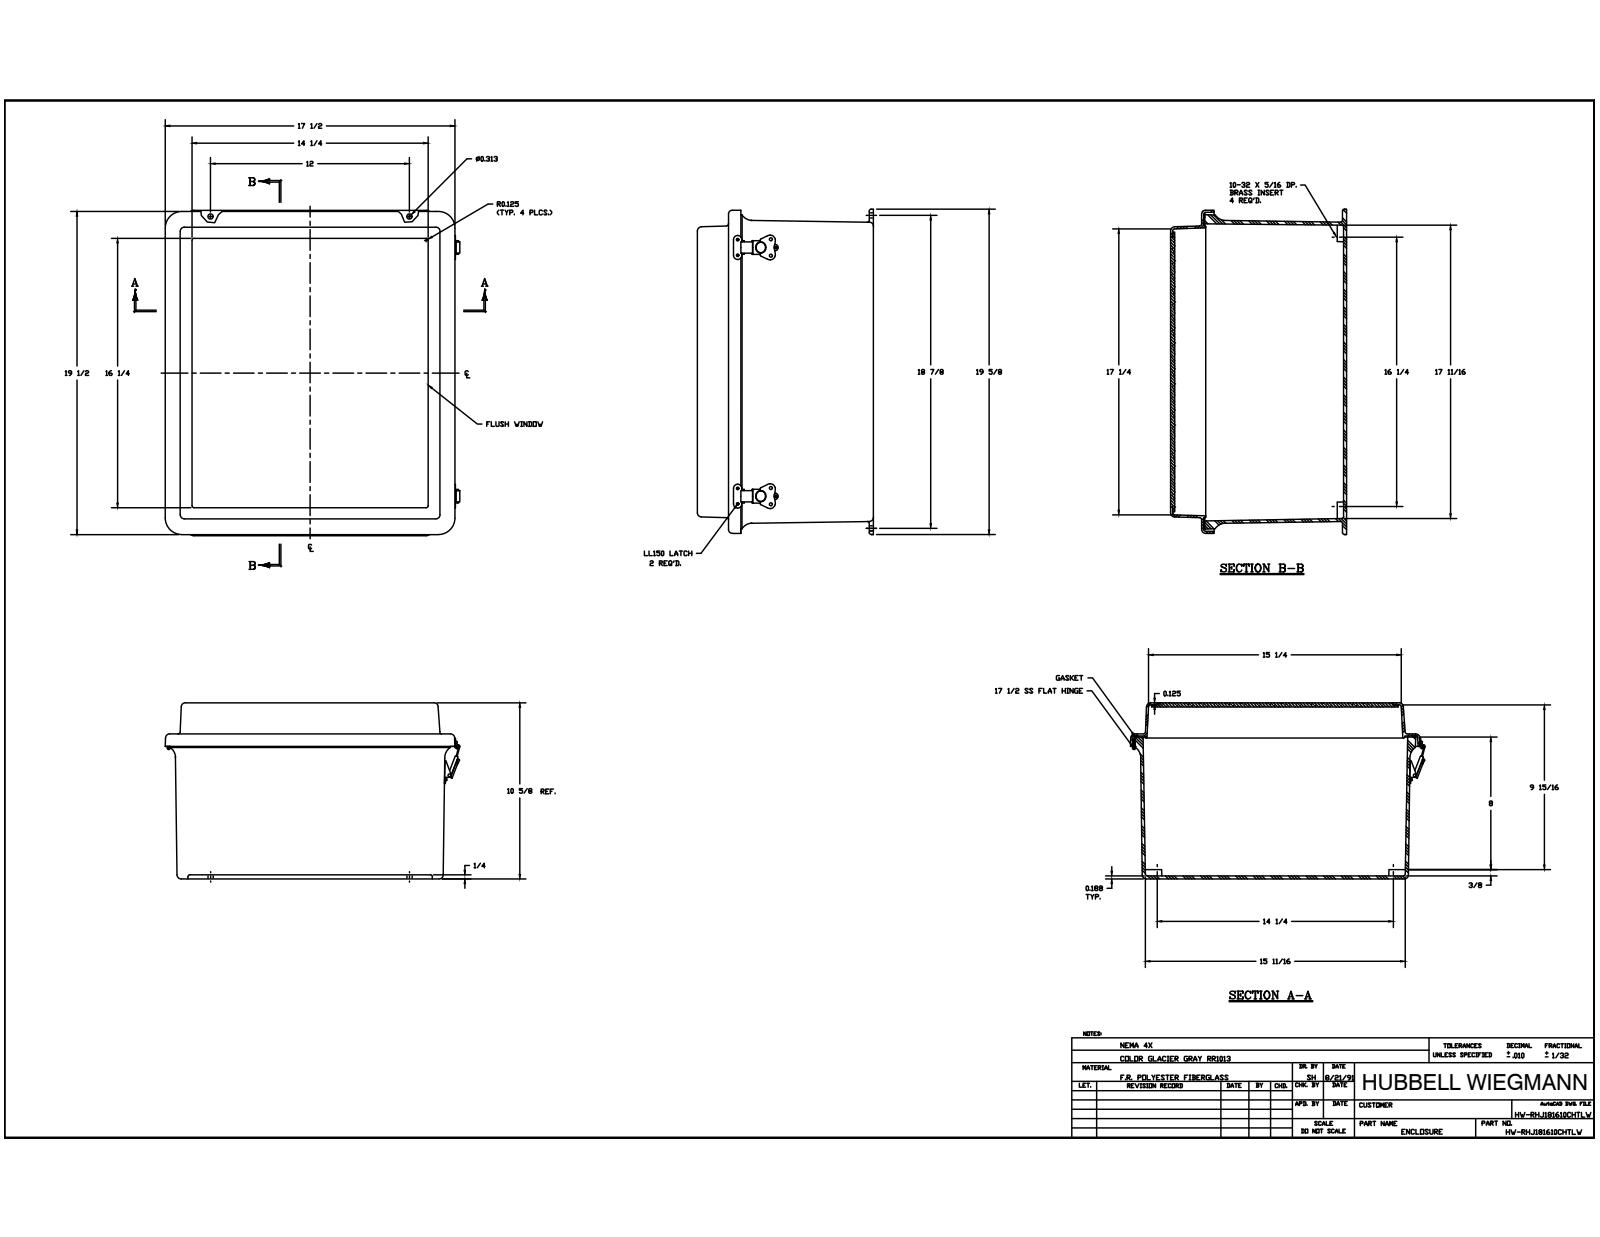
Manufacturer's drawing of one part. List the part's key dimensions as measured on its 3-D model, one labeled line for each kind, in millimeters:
Part name (STEP PRODUCT): J1816HL_1; RMINS45821P_7; RMINS45821P_8; RMINS45821P_9 (+8 more)
STEP written by: Autodesk Inventor 2014 (AUTOMOTIVE_DESIGN)
Units: millimetres
Bodies: 53 solids, 1399 faces (635 planar, 541 cylindrical, 223 other)
Overall size (bounding box): 498.48 × 449.65 × 270.3
Volume: 4 605 000 mm³ · Surface area: 1 942 000 mm²
Round holes (diameter × count): ⌀3.56 ×20, ⌀3.33 ×12, ⌀3.86 ×5, ⌀3.3 ×4, ⌀3.96 ×4, ⌀4.2 ×4, ⌀5 ×4, ⌀5.54 ×4, ⌀3 ×2, ⌀3.5 ×2, ⌀4.61 ×2, ⌀4.62 ×2
Round bosses / shafts (diameter × count): ⌀6.35 ×20, ⌀3.17 ×20, ⌀6.86 ×4, ⌀14.8 ×2, ⌀13.3 ×2, ⌀5.3 ×2, ⌀4.7 ×2, ⌀3.25 ×2
Partial cylindrical surfaces — rounded edges, fillets, slot ends (radius × count): R3.17 ×24, R0.79 ×20, R2 ×19, R6.35 ×16, R0.95 ×8, R1 ×8, R1.15 ×8, R1.2 ×8
Main face-to-face distances: 4.76, 6.35, 263.96, 4.77, 270.31, 265.54, 259.19, 3.17, 44.45, 50.8
Hole centre spacings: 85.72, 85.73, 171.45, 380.6, 260.35, 380.59, 6.35, 247.65
